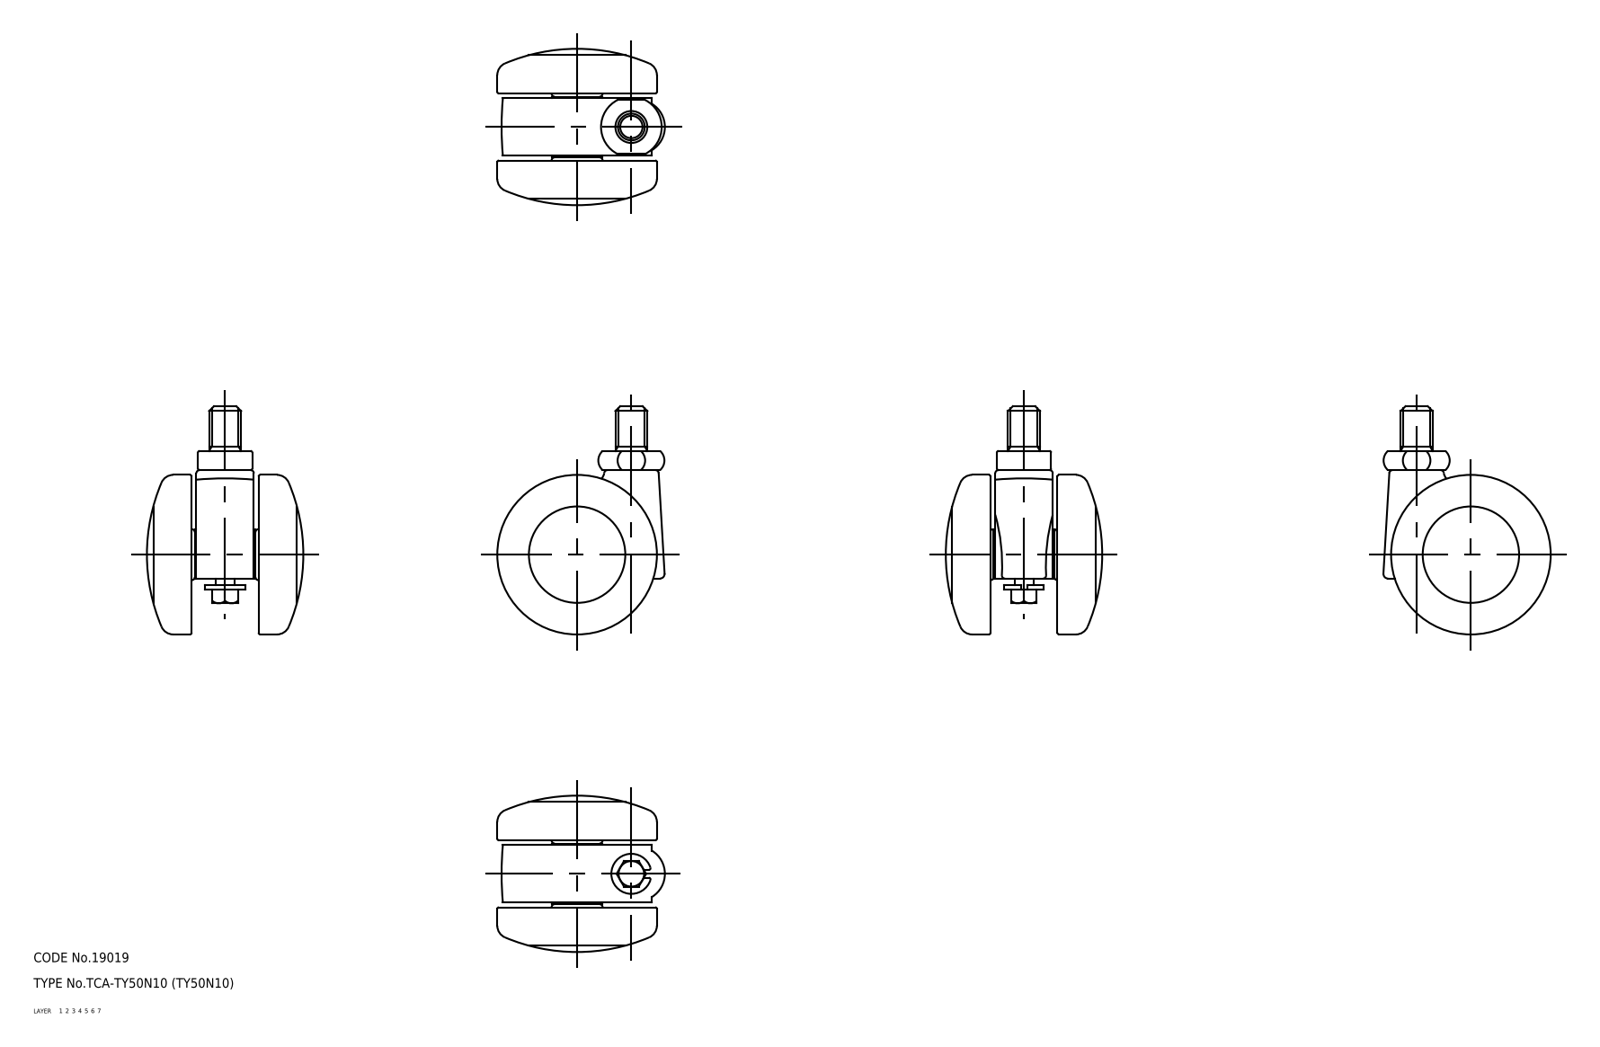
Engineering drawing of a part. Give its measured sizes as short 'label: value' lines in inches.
name: wheel; main shaft; TY50N10_10835_36
written by: CADfix (AUTOMOTIVE_DESIGN)
unit: in
bodies: 4 solids, 124 faces (0 planar, 0 cylindrical, 124 other)
size: 2.815 × 2.064 × 1.929
volume: 3.894 in³; area: 39.47 in²
